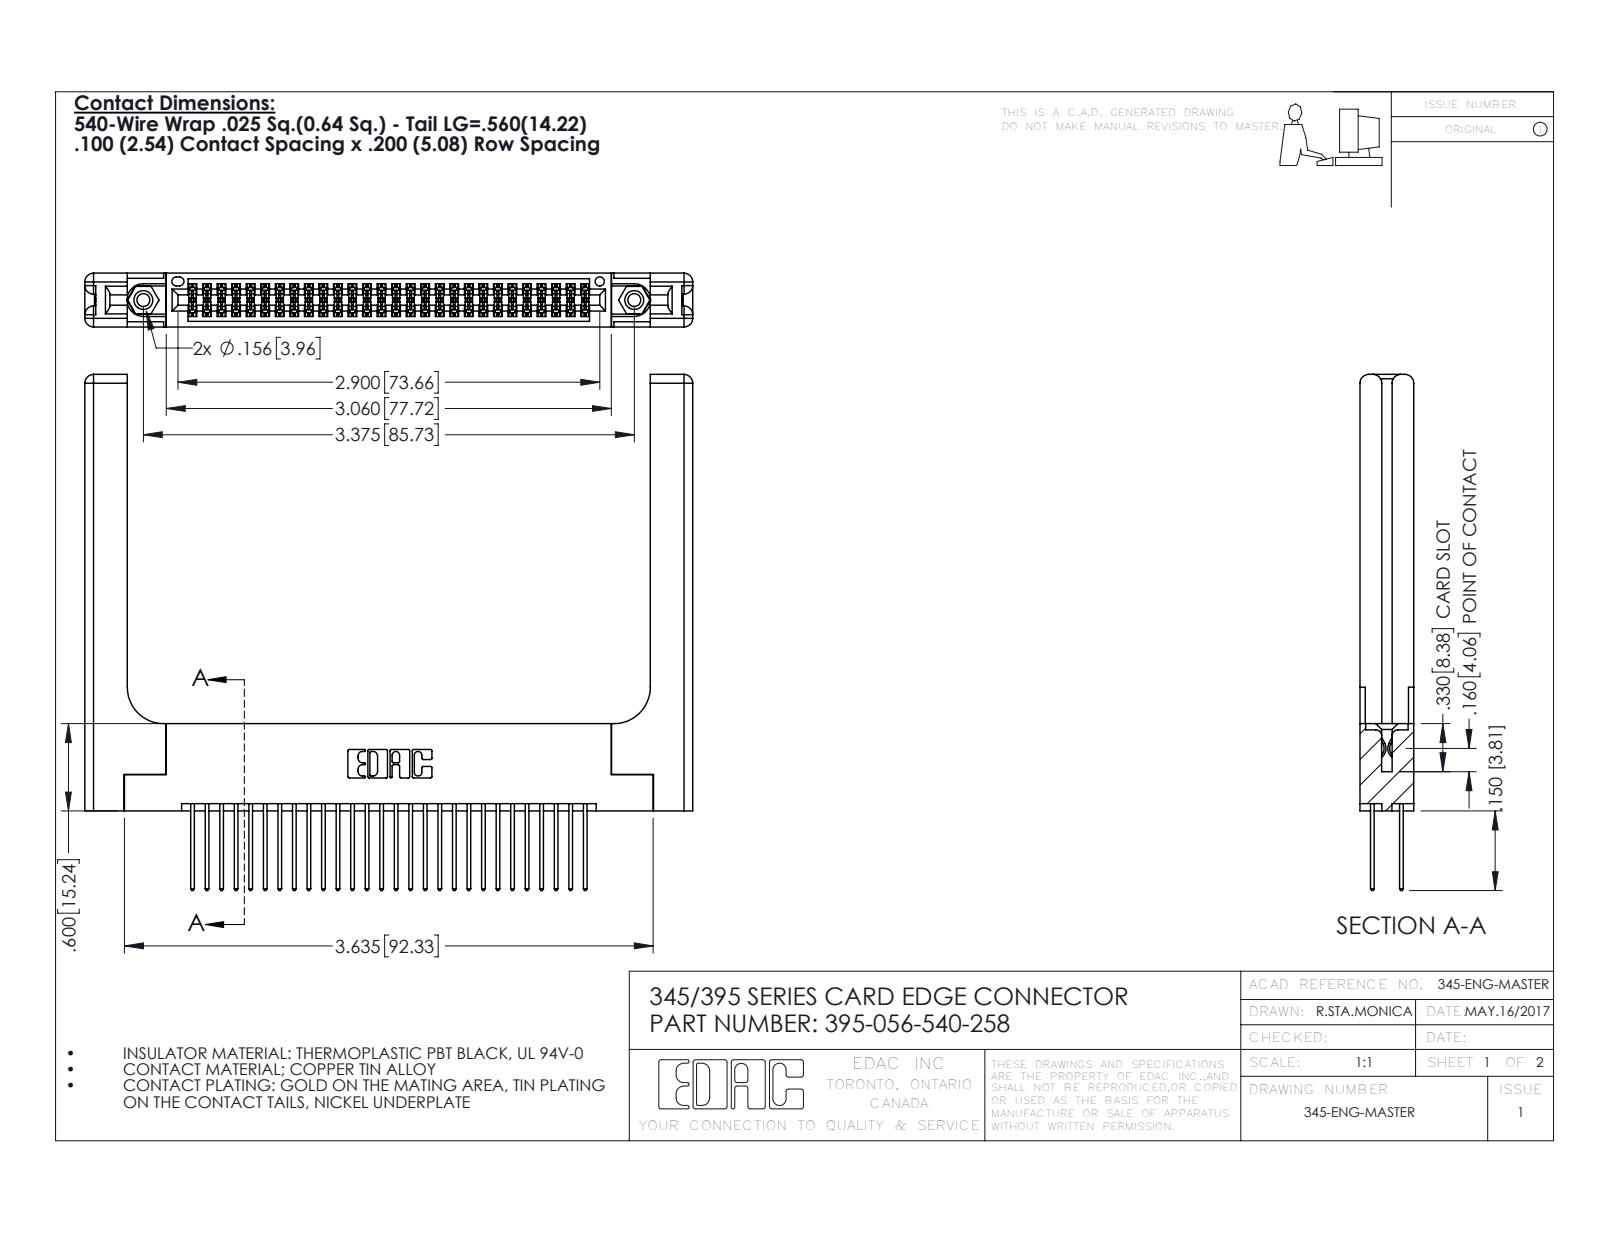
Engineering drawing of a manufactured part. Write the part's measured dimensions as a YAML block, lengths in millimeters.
part_name: "345-220-058_345-220-058; 395-056-540-258; 345 Part_Flush Mounting Lugs - 0.156 Dia-TH; 345-250-001_345-250-001-102 (+1 more)"
step_written_by: "SolidWorks 2016 (CONFIG_CONTROL_DESIGN)"
units: millimeters
bodies: {solids: 61, faces: 3182, planar: 2076, cylindrical: 1046, other: 60}
overall_size: [106.1, 90.1, 9.4]
volume: 18860
surface_area: 21140
round_holes:
  - {diameter: 2.3, count: 2}
  - {diameter: 3.2, count: 2}
  - {diameter: 4, count: 2}
  - {diameter: 1.6, count: 1}
round_bosses_or_shafts:
  - {diameter: 3.9, count: 2}
partial_cylinders:
  - {radius: 0.2, count: 84}
  - {radius: 0.3, count: 56}
  - {radius: 0.3, count: 22}
  - {radius: 1.5, count: 16}
  - {radius: 0.2, count: 6}
  - {radius: 0.8, count: 6}
  - {radius: 0.7, count: 3}
  - {radius: 0.4, count: 2}
face_to_face_distances: [1.8, 7.6, 9.4, 5.1, 2.5, 6.9, 0.6, 5.7, 3.8, 3.8]
hole_center_spacings: [6.9, 79.8, 85.7]
